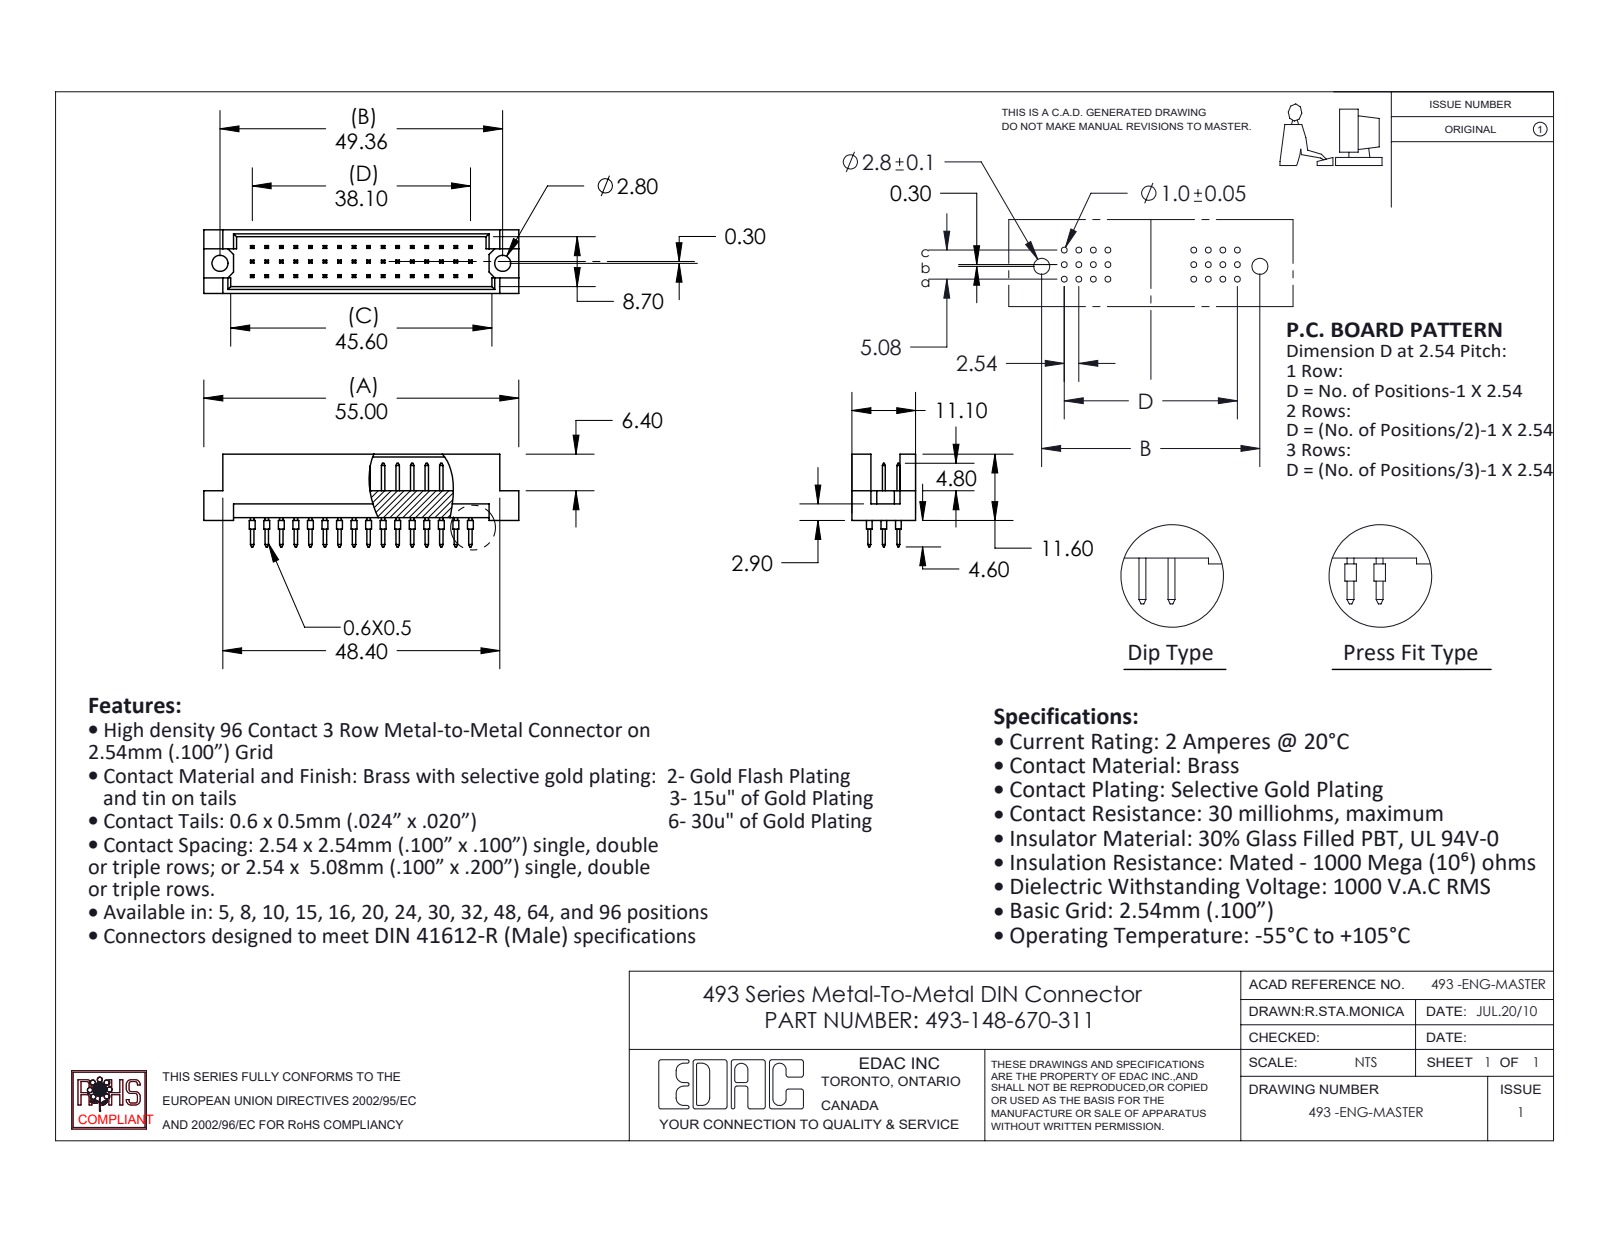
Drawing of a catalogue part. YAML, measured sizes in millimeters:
part_name: "493 Part_48; 493-290_70; 493-148-670-311"
step_written_by: "SolidWorks 2020 (CONFIG_CONTROL_DESIGN)"
units: millimeters
bodies: {solids: 49, faces: 1300, planar: 1200, cylindrical: 100, other: 0}
overall_size: [55, 16.2, 11.1]
volume: 3512
surface_area: 5394
round_holes:
  - {diameter: 2.8, count: 2}
round_bosses_or_shafts:
  - {diameter: 1, count: 48}
face_to_face_distances: [2.54, 1.2, 9.9, 5.08, 0.5, 11.1, 8.7, 4.7, 7.62, 4.6]
hole_center_spacings: [49.36]
